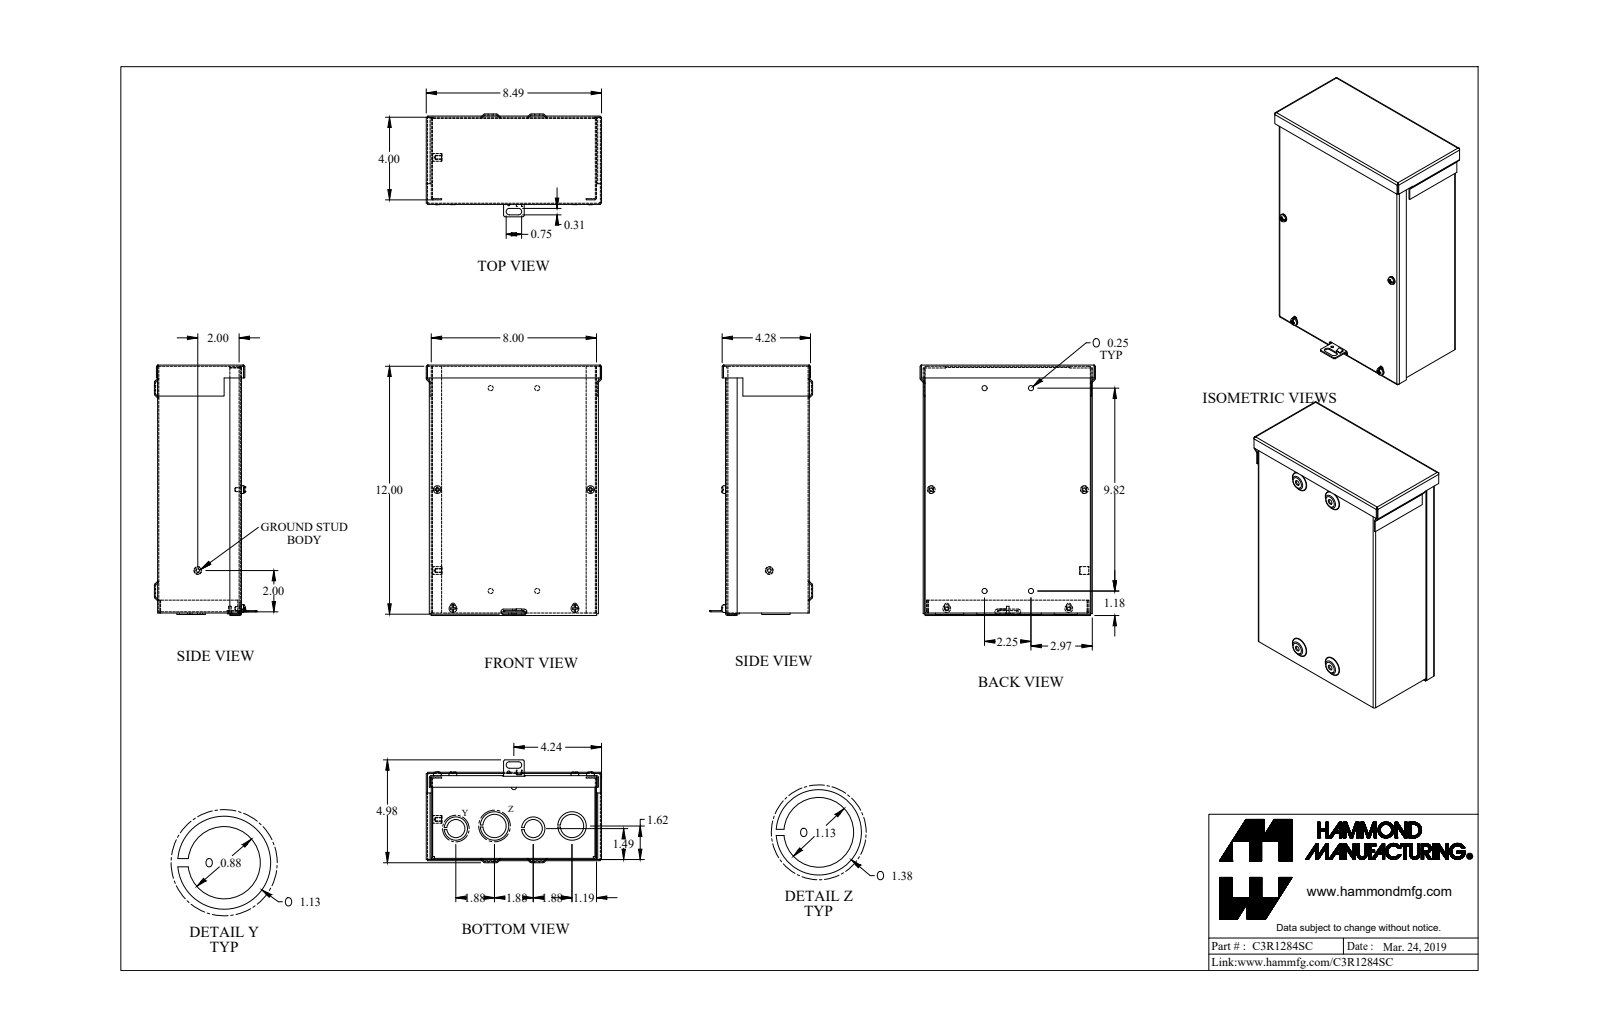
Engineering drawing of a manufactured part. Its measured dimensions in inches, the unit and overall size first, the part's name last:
Units: inches
Overall size (bounding box): 12.12 × 8.489 × 4.977
Round holes (diameter × count): ⌀0.17 ×4, ⌀0.25 ×4, ⌀1.125 ×2, ⌀0.125 ×1, ⌀0.137 ×1, ⌀0.156 ×1, ⌀0.875 ×1, ⌀0.875 ×1
Round bosses / shafts (diameter × count): ⌀0.375 ×4, ⌀0.19 ×4, ⌀1.375 ×2, ⌀1.125 ×2, ⌀0.375 ×1, ⌀0.125 ×1
Partial cylindrical surfaces — rounded edges, fillets, slot ends (radius × count): R0.029 ×21, R0.086 ×21, R0.109 ×8, R0.125 ×8, R0.156 ×2
Main face-to-face distances: 0.057, 4, 3.943, 4.057, 7.943, 0.057, 8, 7.886, 11.886, 11.943
Hole centre spacings: 5.547, 6.888, 1.88, 1.998, 2.25, 3.75, 4.165, 5.726
Volume: 23.88 in³ · Surface area: 844.7 in²
Bodies: 11 solids, 424 faces (223 planar, 115 cylindrical, 86 other)
Part name (STEP PRODUCT): C3R1284SC_Default
STEP written by: SolidWorks 2019 (CONFIG_CONTROL_DESIGN)
